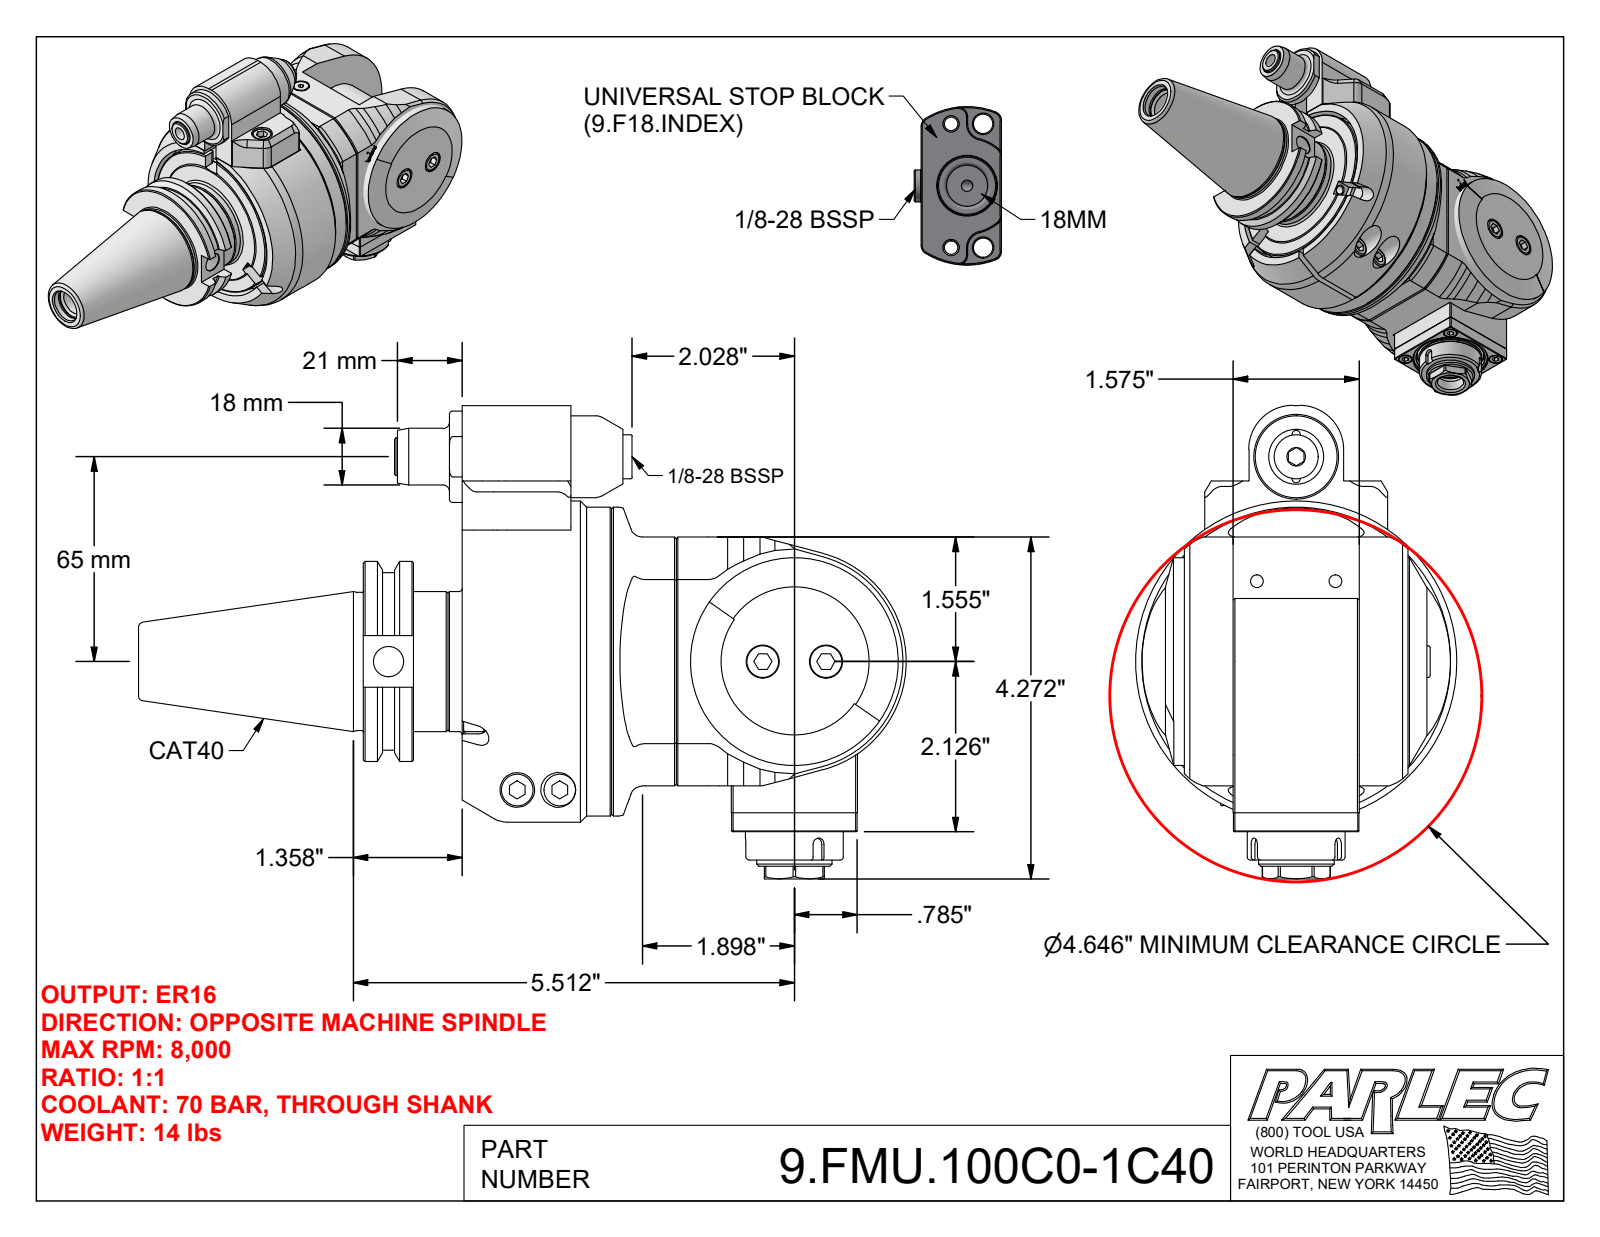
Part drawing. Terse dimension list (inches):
name: 9.FMU.100C0-1C40; FMU-10C; 9_GA1_446_2 (Type 1, C40, 65mm)
written by: Autodesk Inventor 2022 (AUTOMOTIVE_DESIGN)
unit: in
bodies: 6 solids, 622 faces (305 planar, 136 cylindrical, 181 other)
size: 9.596 × 5.915 × 4.016
volume: 62.24 in³; area: 261.2 in²
holes: 5× ⌀0.276, 3× ⌀0.413, 3× ⌀0.433, 2× ⌀0.102, 2× ⌀0.157, 2× ⌀0.165, 2× ⌀0.197, 2× ⌀0.409, 1× ⌀0.098, 1× ⌀0.118, 1× ⌀0.256, 1× ⌀0.335
bosses: 7× ⌀0.394, 4× ⌀0.236, 2× ⌀0.315, 1× ⌀4.016, 1× ⌀3.858, 1× ⌀3.031, 1× ⌀2.598, 1× ⌀2.5
rounds: 6× R0.157, 3× R0.079, 2× R0.02, 2× R0.039, 2× R0.138, 2× R0.197, 2× R0.551, 1× R0.423
face distances: 0.531, 1.575, 2.106, 1.26, 0.61, 2.185, 2.717, 0.315, 0.02, 3.031
hole spacings: 0.886, 1.253, 0.276, 0.394, 0.872, 0.9, 1.118, 1.371
